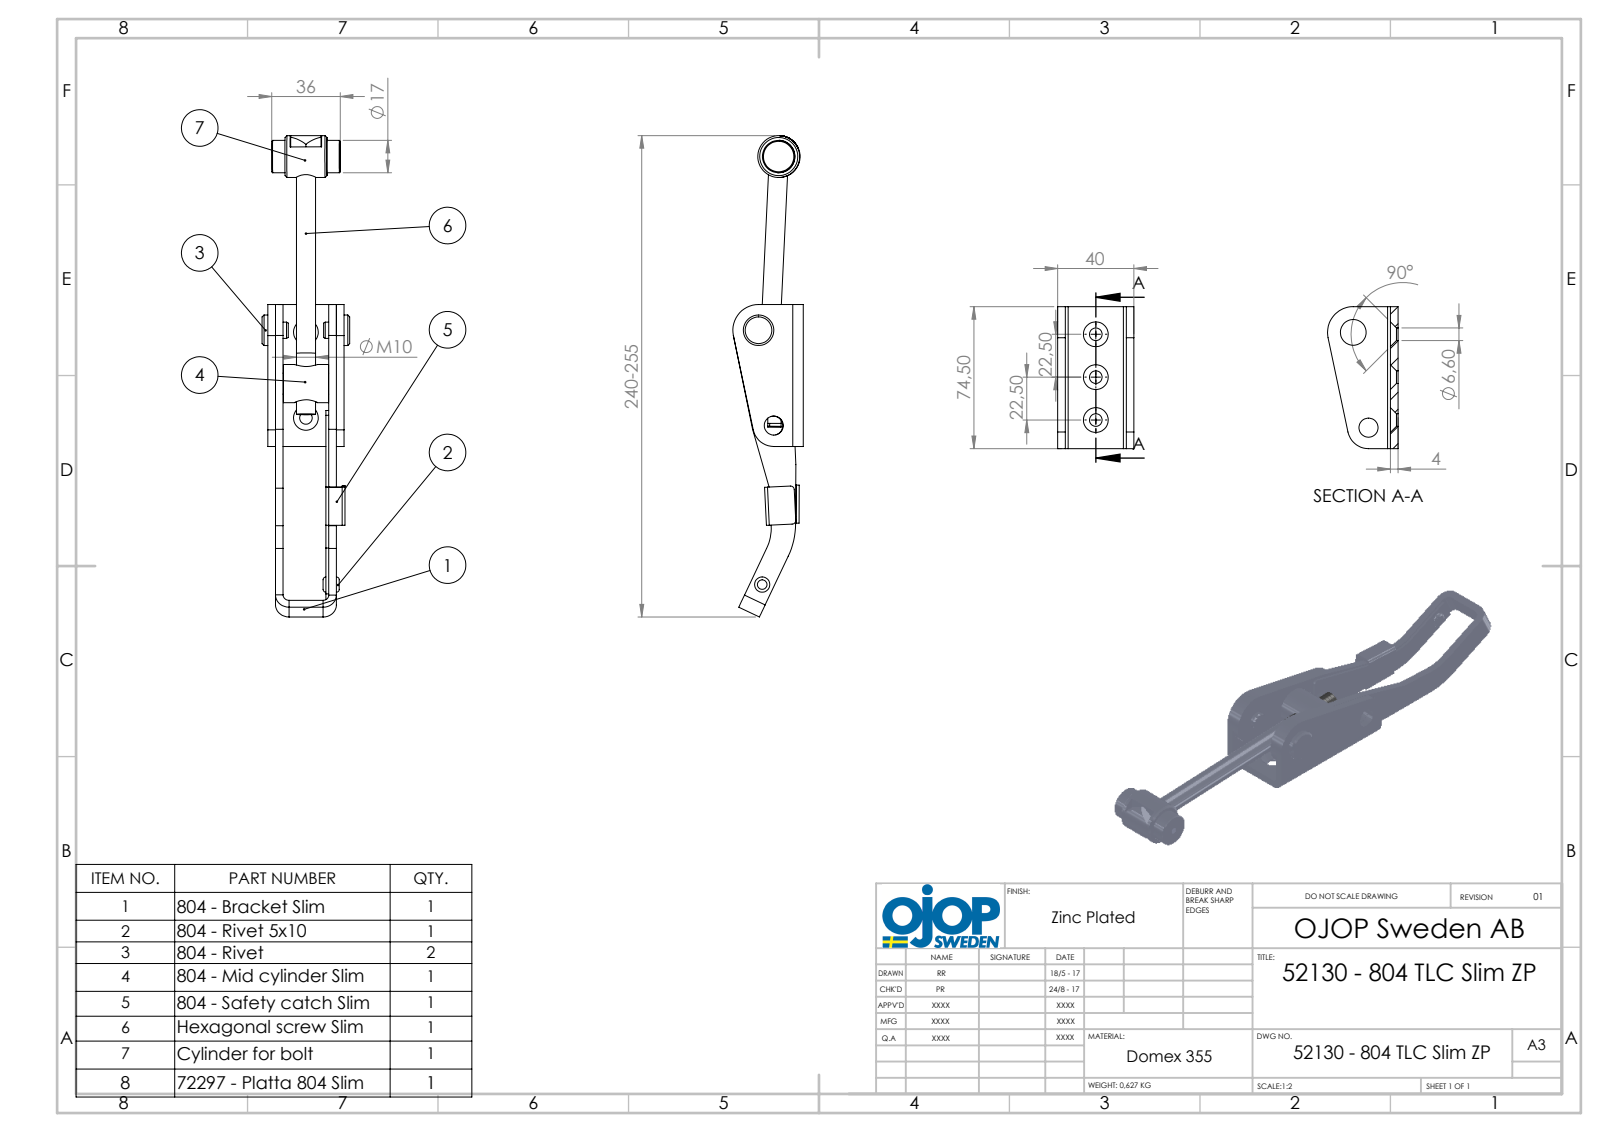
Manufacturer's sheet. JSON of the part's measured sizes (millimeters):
{"part_name": "62080 - Rulle 804 Slim; 62035 - Ansatsnit 10,9x5,7x8,5x8,0 FZB(804); 62030 - Nit Stål KN 5x10 GL 804; 72139 - Bygel 804 Slim (+5 more)", "step_written_by": "SolidWorks 2015 (AUTOMOTIVE_DESIGN)", "units": "millimeters", "bodies": {"solids": 9, "faces": 234, "planar": 100, "cylindrical": 100, "other": 34}, "overall_size": [252.62, 46, 37], "volume_mm3": 80910, "surface_area_mm2": 47399, "round_holes": [[6.6, 3], [10, 2], [3.3, 1], [4.97, 1], [5.1, 1], [8.6, 1], [9.3, 1], [10.3, 1], [11.2, 1], [13.5, 1]], "round_bosses_or_shafts": [[17, 2], [22, 1], [20, 1], [16, 1], [11, 1], [10.9, 1], [10.01, 1], [10, 1]], "partial_cylinders_radius": [[1.5, 6], [0.5, 4], [2, 4], [5.5, 2], [3, 1], [3.17, 1], [7, 1], [7.17, 1]], "face_to_face_distances": [4, 32, 28, 36, 8, 24, 1.5, 40, 5.5, 9.5], "hole_center_spacings": [22.5, 22.23, 22.27, 28.41, 45, 50.64, 50.66, 83.58]}
